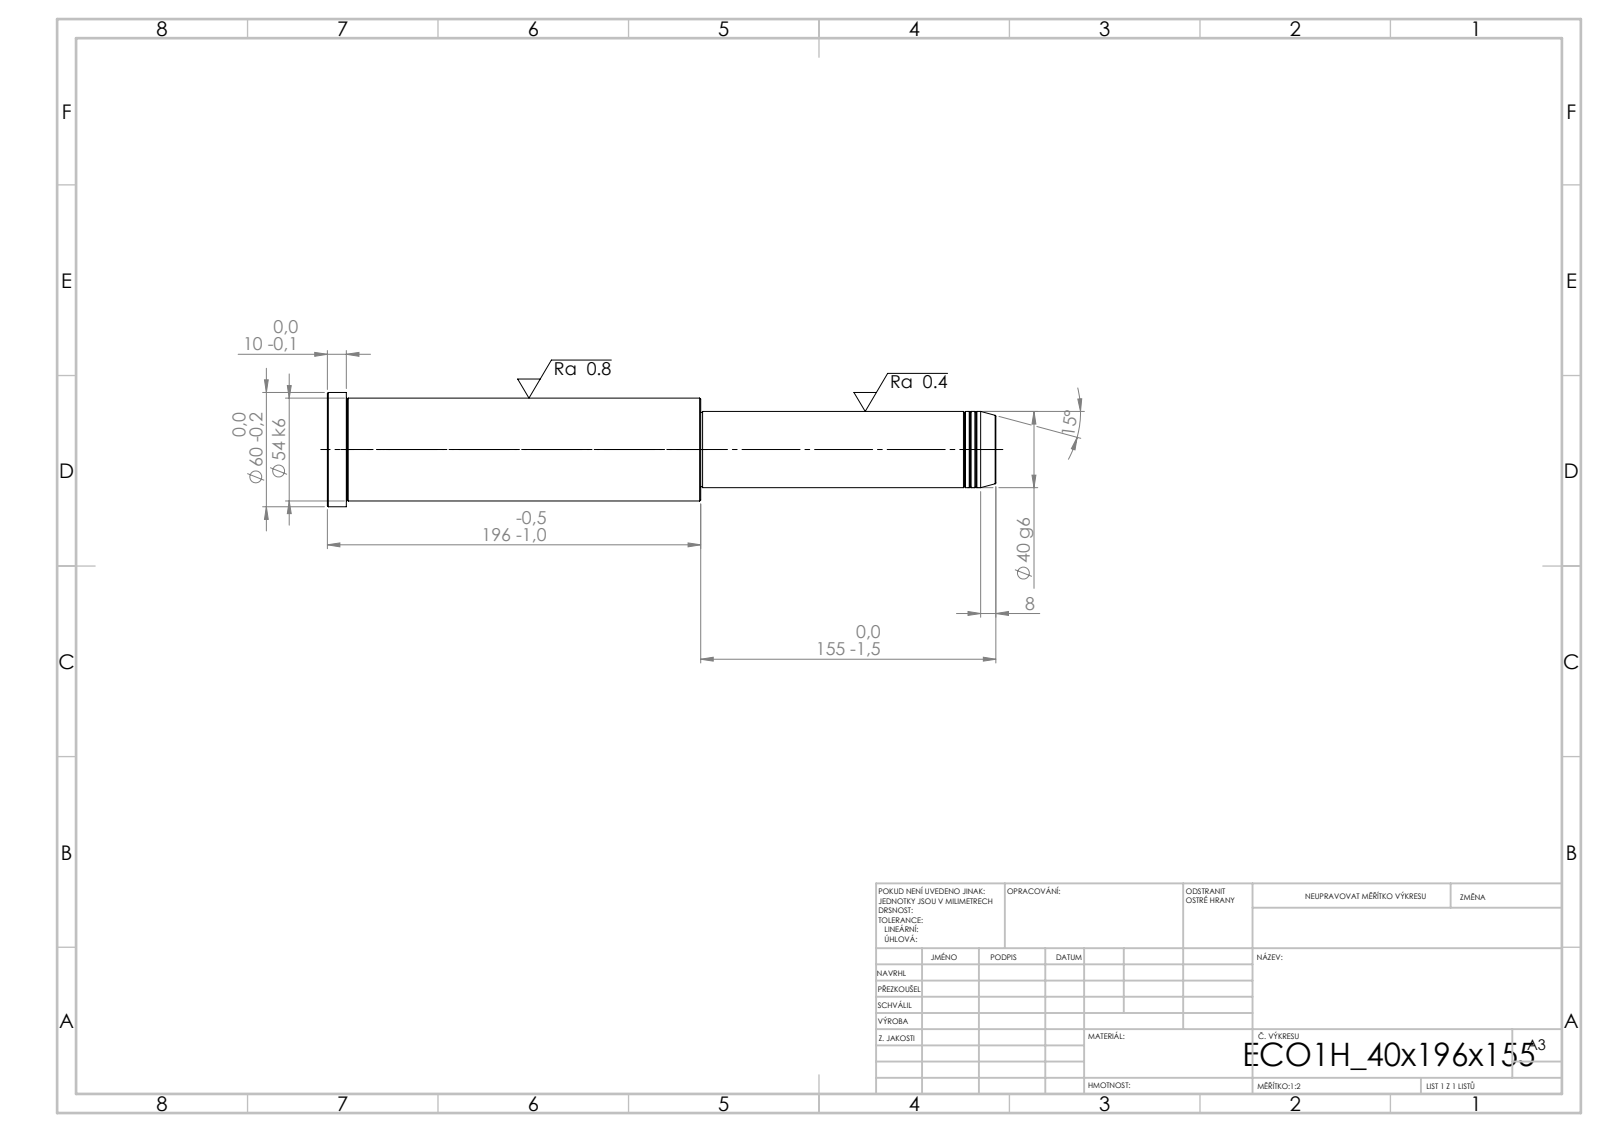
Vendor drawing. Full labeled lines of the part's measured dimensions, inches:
STEP written by: SolidWorks 2019 (CONFIG_CONTROL_DESIGN)
Units: inches
Bodies: 1 solid, 43 faces (5 planar, 14 cylindrical, 24 other)
Overall size (bounding box): 13.819 × 2.362 × 2.362
Volume: 39.52 in³ · Surface area: 90.83 in²
Round bosses / shafts (diameter × count): ⌀2.362 ×1, ⌀2.126 ×1, ⌀1.575 ×1, ⌀1.535 ×1
Main face-to-face distances: 7.717, 6.102, 13.819, 13.425, 7.323, 0.394, 6.063, 0.039, 7.362, 7.756
